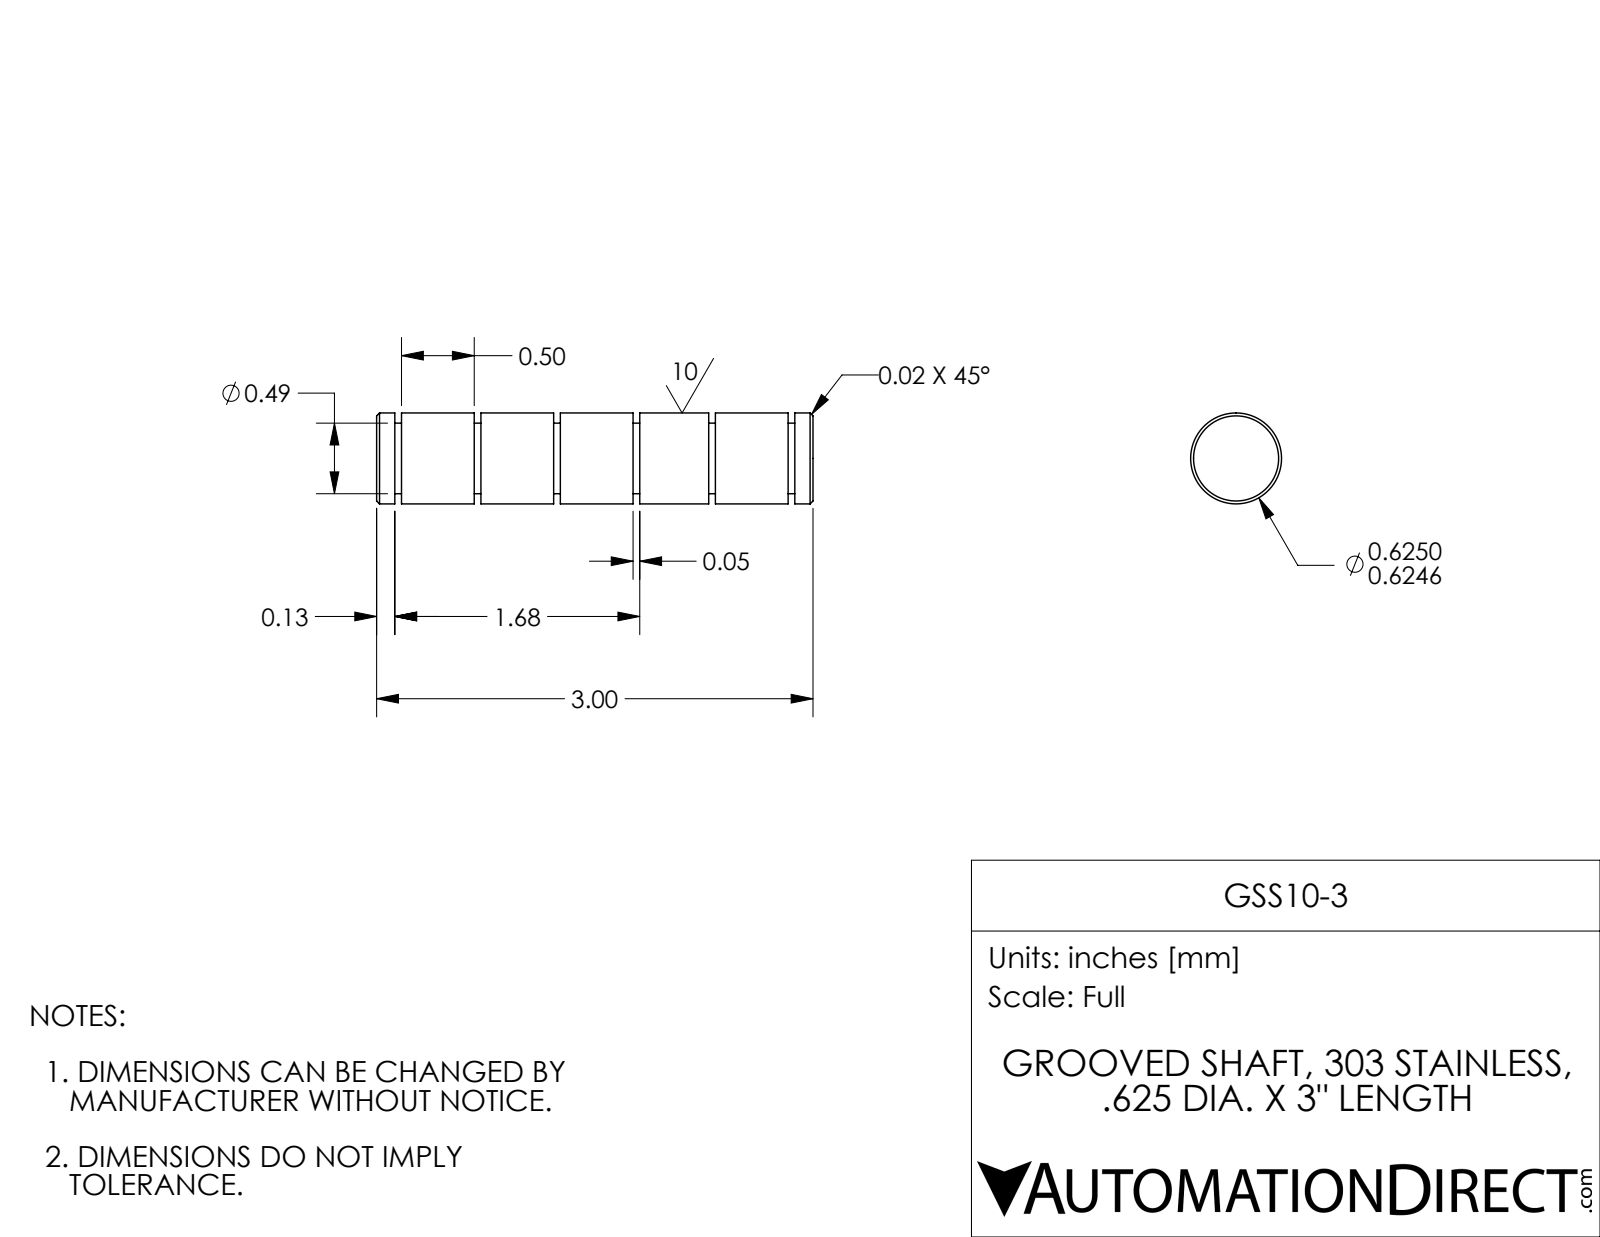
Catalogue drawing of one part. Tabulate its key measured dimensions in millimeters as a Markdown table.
| quantity | value |
| --- | --- |
| part name | GSS10-3 |
| STEP written by | SolidWorks 2017 (AUTOMOTIVE_DESIGN) |
| units | millimeters |
| bodies | 1 solid, 44 faces (14 planar, 26 cylindrical, 4 other) |
| overall size | 76.2 × 15.9 × 15.9 |
| volume | 14 500 mm³ |
| surface area | 5 032 mm² |
| round bosses / shafts (diameter × count) | 15.9 × 1, 12.3 × 1 |
| main face-to-face distances | 13.9, 1.2, 27.7, 12.7, 15, 54.8, 40.9, 27.1, 76.2, 4.3 |
